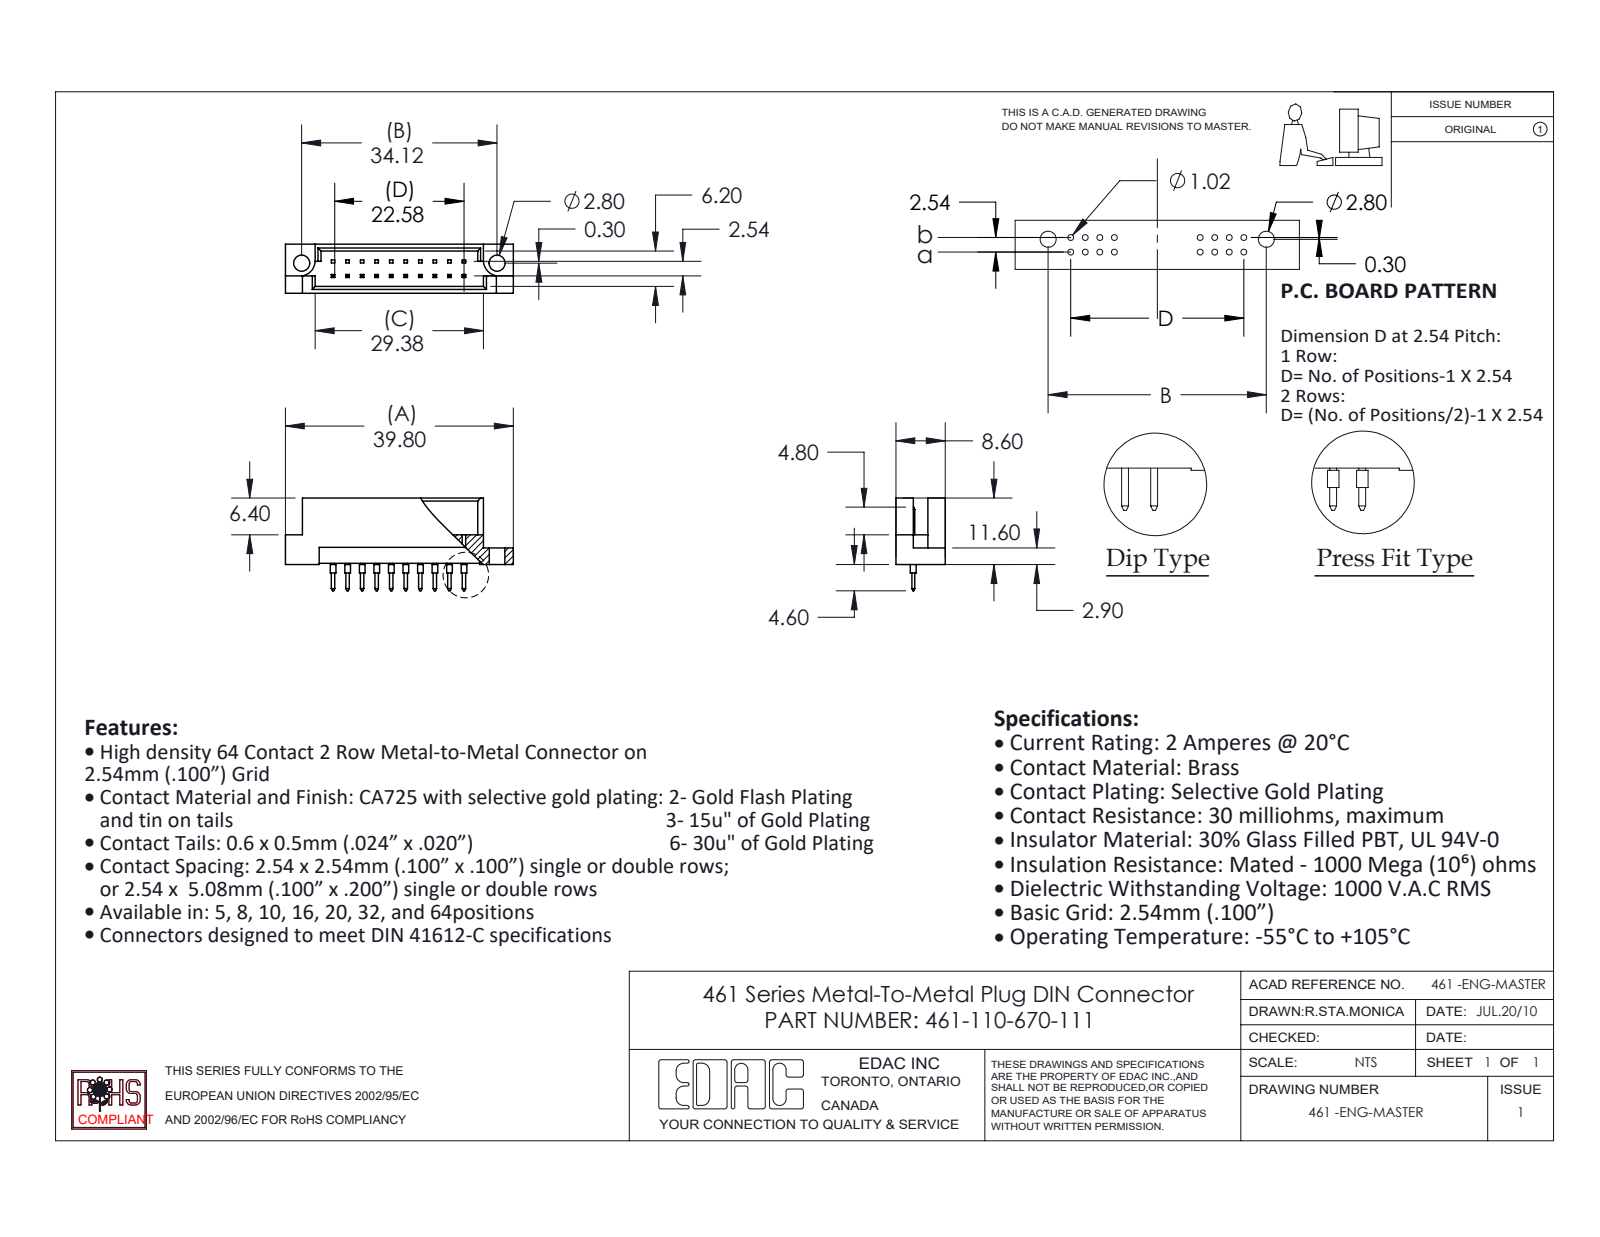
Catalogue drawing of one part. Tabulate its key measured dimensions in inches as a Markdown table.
| quantity | value |
| --- | --- |
| part name | 461-110-670-111; 461-290_70; 461 Part_20 |
| STEP written by | SolidWorks 2020 (CONFIG_CONTROL_DESIGN) |
| units | inches |
| bodies | 11 solids, 348 faces (322 planar, 26 cylindrical, 0 other) |
| overall size | 1.567 × 0.638 × 0.339 |
| volume | 0.119 in³ |
| surface area | 4.152 in² |
| round holes (diameter × count) | 0.11 × 2 |
| round bosses / shafts (diameter × count) | 0.039 × 10 |
| partial cylindrical surfaces (radius × count) | 0.11 × 2 |
| main face-to-face distances | 0.047, 0.291, 0.339, 0.244, 0.1, 0.197, 0.062, 0.109, 0.129, 0.209 |
| hole center spacings | 1.343 |
